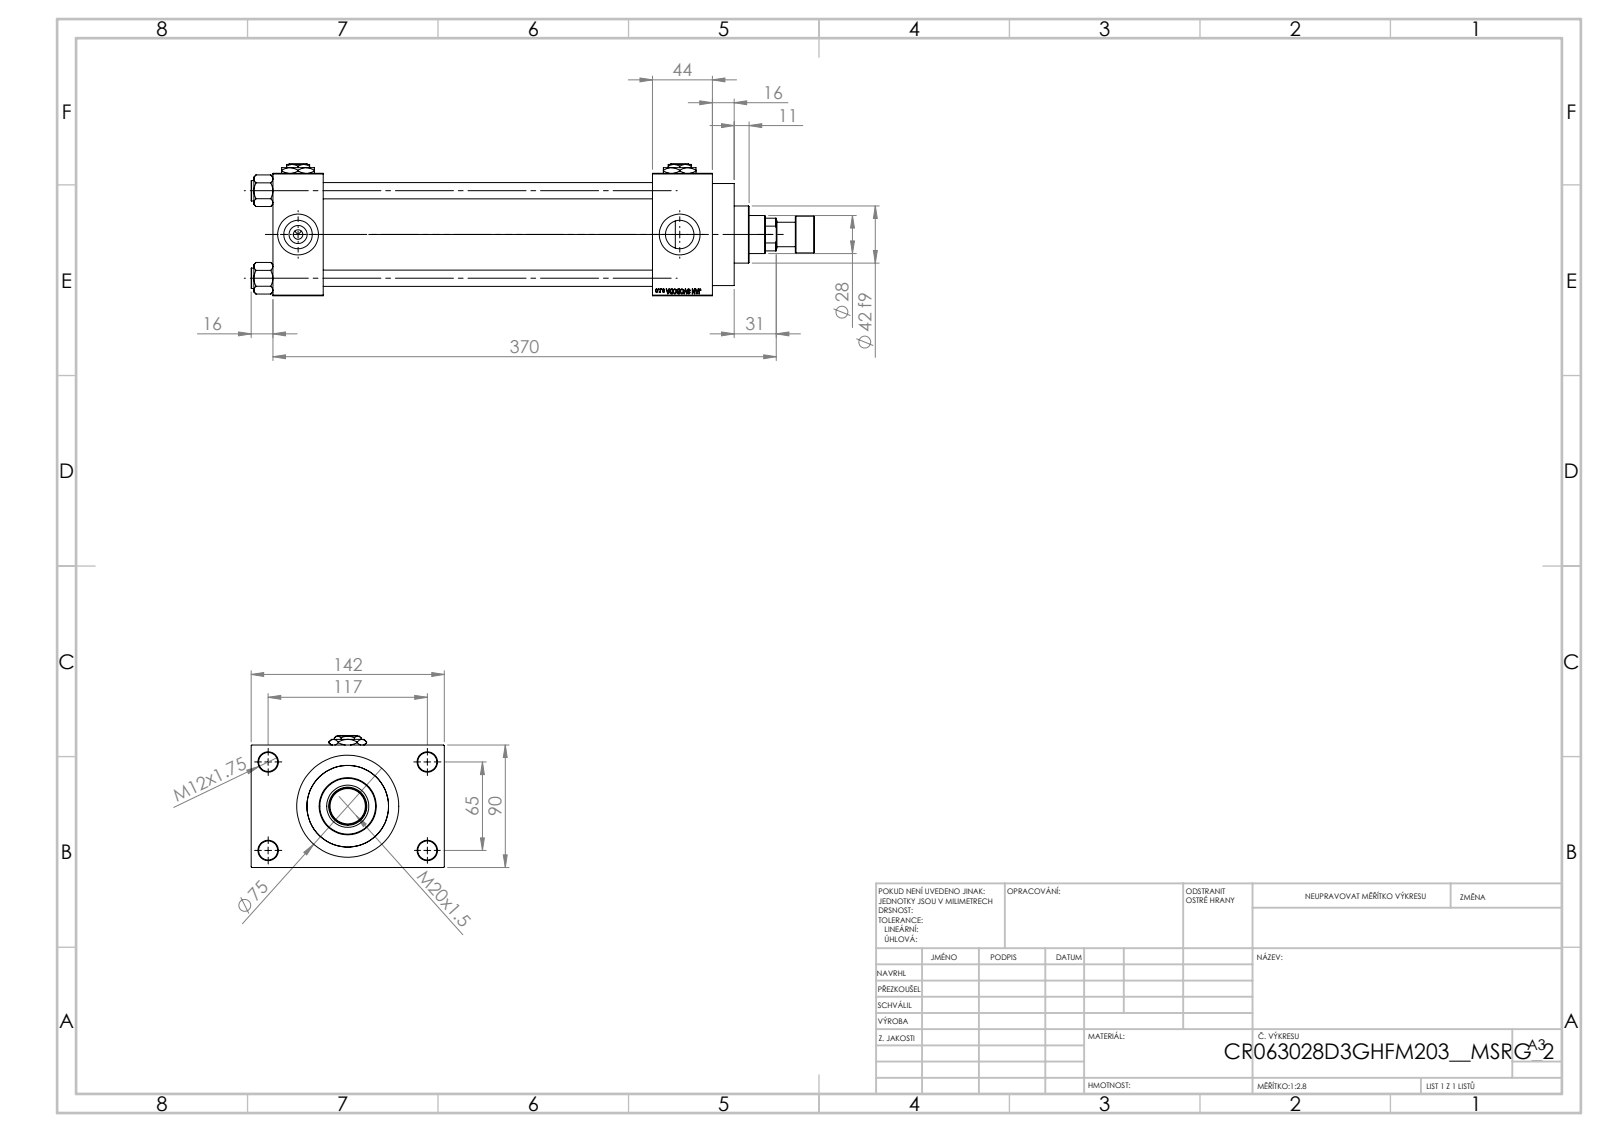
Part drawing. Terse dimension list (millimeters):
name: V215CR_VCP_D; NUT_M5_D; V215_VC_A; V215CR_ROD_END_F (+3 more)
written by: SolidWorks 2019 (CONFIG_CONTROL_DESIGN)
unit: mm
bodies: 14 solids, 1218 faces (549 planar, 103 cylindrical, 566 other)
size: 414 × 142 × 97
volume: 1 412 000 mm³; area: 327 780 mm²
holes: 4× ⌀12, 4× ⌀14, 4× ⌀20.96, 4× ⌀30, 3× ⌀7, 1× ⌀18.5, 1× ⌀28, 1× ⌀31, 1× ⌀50, 1× ⌀60, 1× ⌀63
bosses: 4× ⌀15, 1× ⌀75, 1× ⌀69, 1× ⌀42, 1× ⌀27, 1× ⌀18
face distances: 90, 242, 37, 279, 286, 323, 44, 26, 116, 16
hole spacings: 26.35, 45.47, 64.3, 66.92, 69.81, 90.65, 111.34, 65
